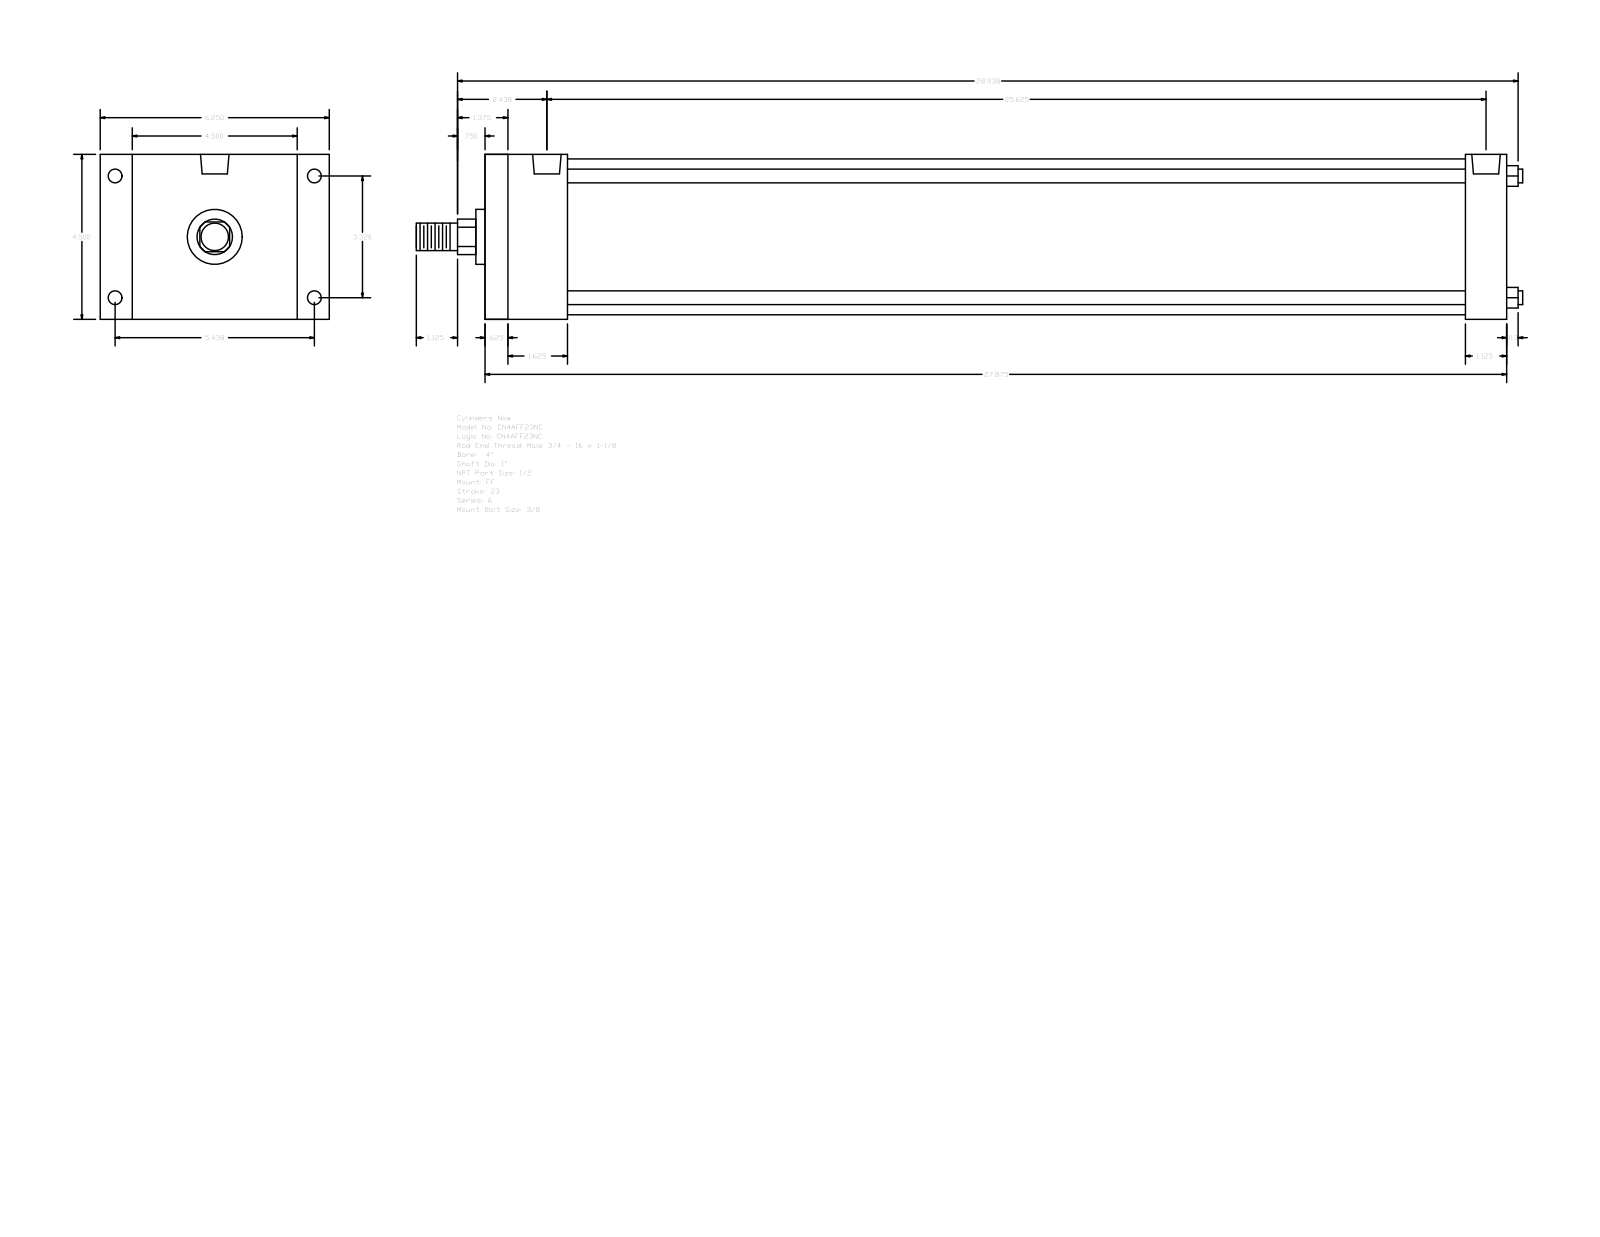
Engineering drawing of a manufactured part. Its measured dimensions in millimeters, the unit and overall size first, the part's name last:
Units: millimetres
Overall size (bounding box): 766.76 × 158.75 × 114.3
Round holes (diameter × count): ⌀8.73 ×4, ⌀9.53 ×4, ⌀19.77 ×2
Round bosses / shafts (diameter × count): ⌀9.53 ×4, ⌀107.95 ×1, ⌀38.1 ×1, ⌀25.4 ×1, ⌀19.05 ×1
Partial cylindrical surfaces — rounded edges, fillets, slot ends (radius × count): R12.29 ×1
Main face-to-face distances: 114.3, 708.03, 15.87, 692.16, 22.23, 136.53, 679.45, 663.58, 28.58, 57.15
Hole centre spacings: 3.18, 84.32, 138.12, 161.82, 644.52, 647.7, 650.88
Bodies: 0 solids, 92 faces (64 planar, 28 cylindrical, 0 other)
Part name (STEP PRODUCT): A_FF__0400_1
STEP written by: GSSL Pune (CONFIG_CONTROL_DESIGN)
